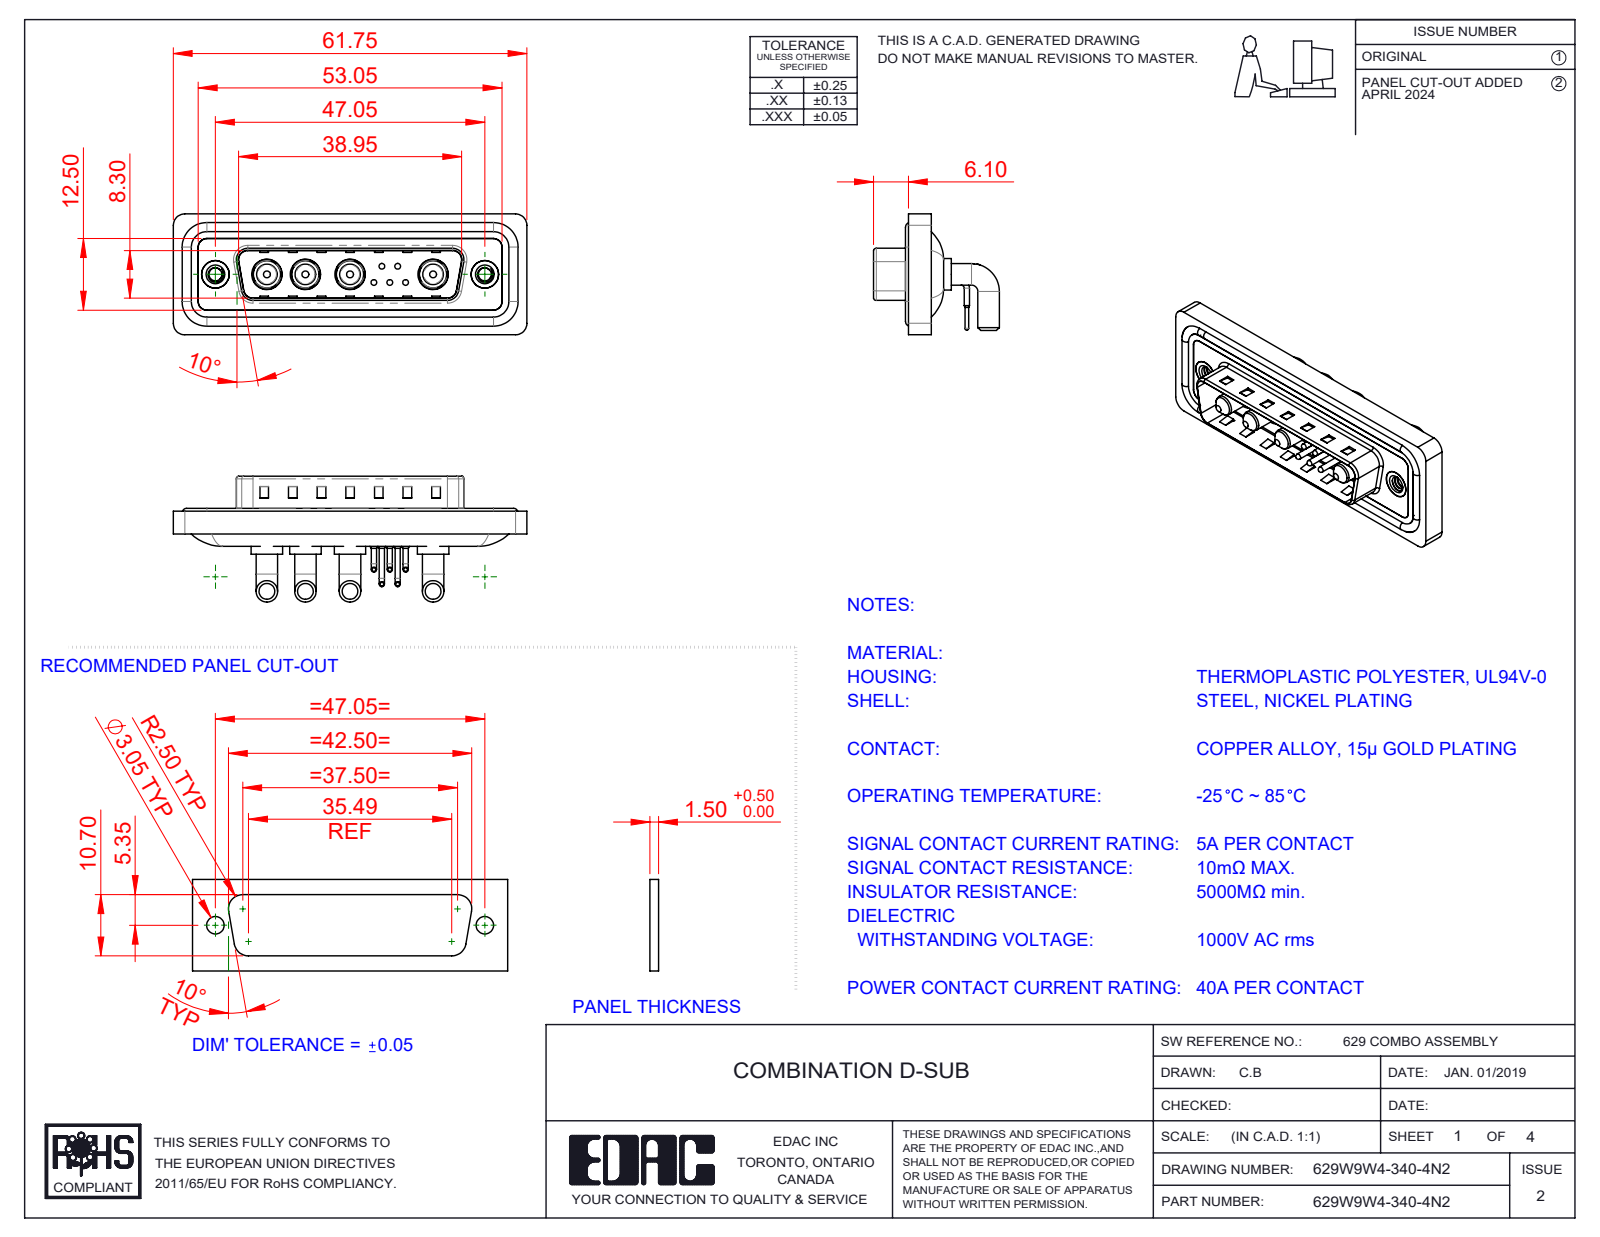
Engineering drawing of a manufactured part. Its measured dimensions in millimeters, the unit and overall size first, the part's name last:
Units: millimetres
Overall size (bounding box): 61.75 × 21.98 × 21.1
Round holes (diameter × count): ⌀0.75 ×5, ⌀1.6 ×5, ⌀2 ×5, ⌀4.85 ×4, ⌀5.3 ×4, ⌀2.26 ×2, ⌀4 ×2, ⌀4.8 ×2, ⌀5 ×2
Round bosses / shafts (diameter × count): ⌀0.9 ×10, ⌀3.75 ×8, ⌀1.5 ×5, ⌀1 ×5, ⌀0.65 ×5, ⌀5.5 ×4, ⌀5.2 ×4, ⌀4.75 ×4
Partial cylindrical surfaces — rounded edges, fillets, slot ends (radius × count): R1.5 ×18, R2 ×18, R0.5 ×8, R1.6 ×8, R1.01 ×5, R0.25 ×4, R0.6 ×4, R0.65 ×4
Main face-to-face distances: 0.4, 2.9, 0.8, 4.1, 1.1, 4.5, 2.1, 1.6, 3.1, 6
Hole centre spacings: 3.16, 2.77, 5.04, 14.5, 2.78, 4.4, 4.41, 5
Volume: 8 007 mm³ · Surface area: 12 552 mm²
Bodies: 20 solids, 1205 faces (569 planar, 452 cylindrical, 184 other)
Part name (STEP PRODUCT): 629Combo Threaded Rivet_2; 629Combo Housing_9W4; 629W9W4-340-4N2; 629Combo Shell Front_25 Contacts (+5 more)
STEP written by: SolidWorks 2023 (CONFIG_CONTROL_DESIGN)
